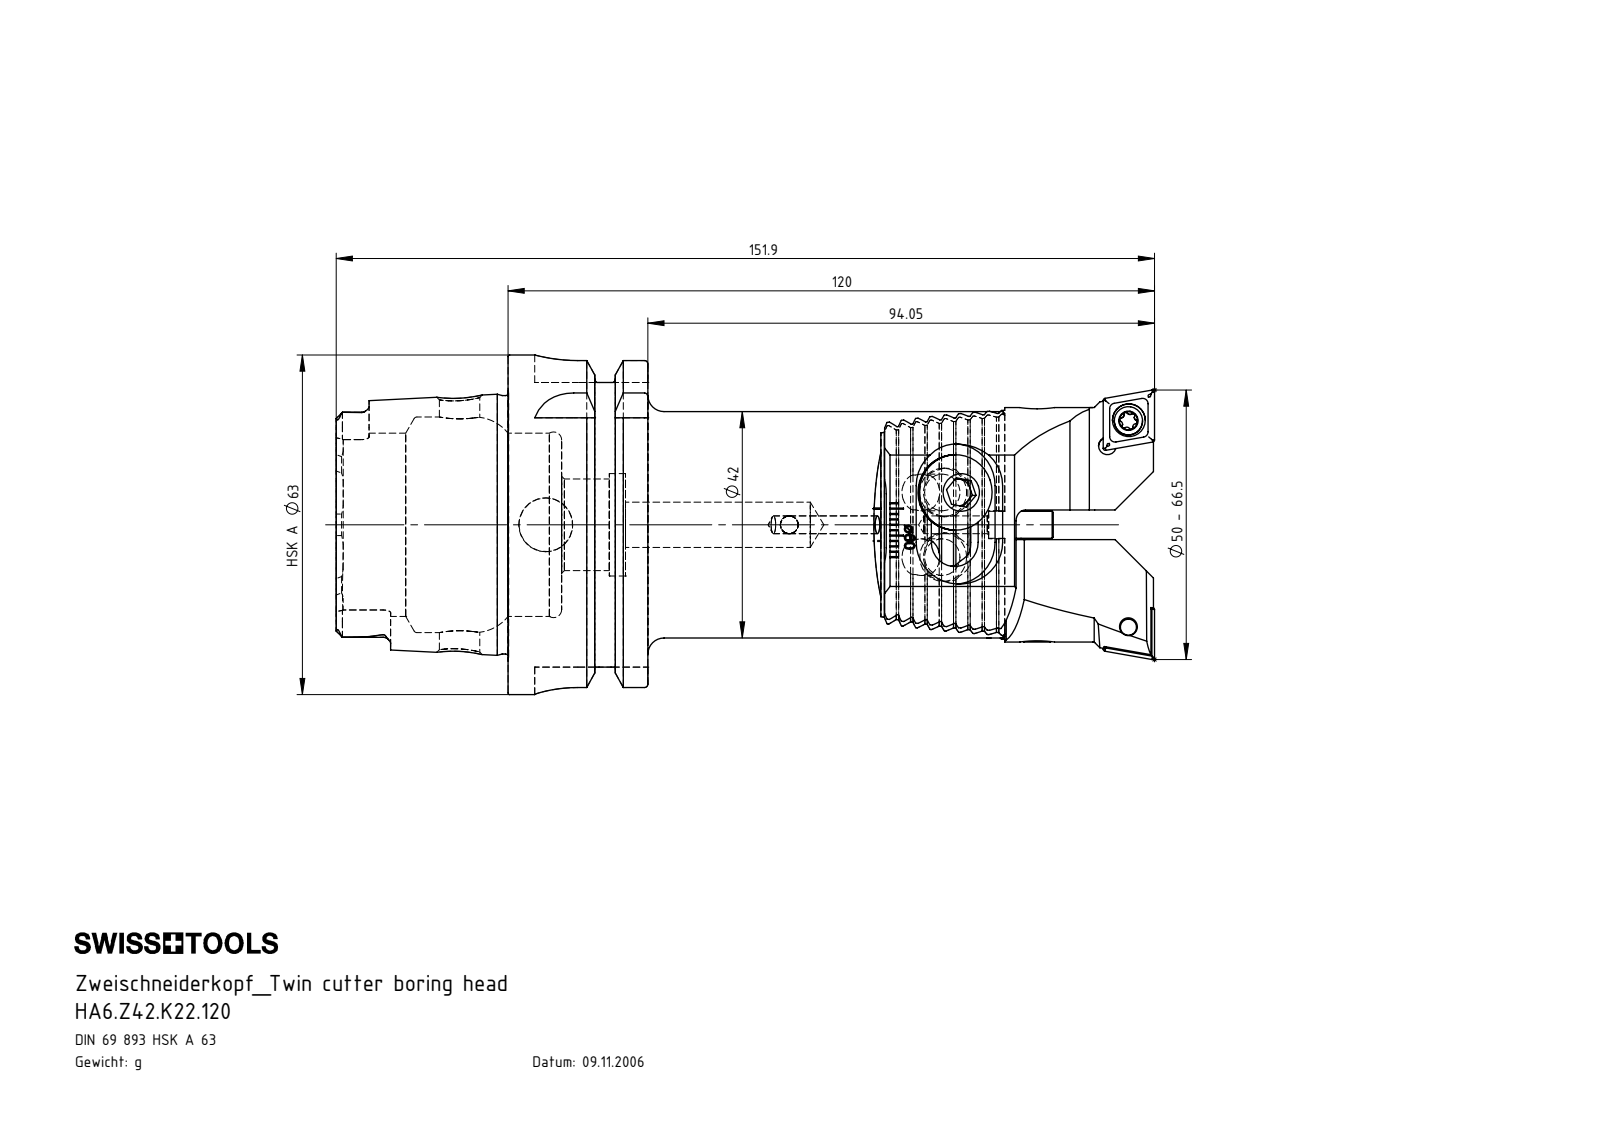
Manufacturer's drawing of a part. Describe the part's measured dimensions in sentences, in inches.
The part is named "HA6.Z42.K22.120; Z42-ER1.002.020_A; Z42-ER1.001.020; Z42-ER1.003.020_A_gespannt (+1 more)". Its 3-D file was written by "SolidWorks 2022 (CONFIG_CONTROL_DESIGN)". It is 5 solids with 408 faces: 183 planar, 120 cylindrical and 105 other. Overall it measures 4.886 by 2.48 by 2.48 inches. Its volume is 9.513 cubic inches and its surface area 55.14 square inches. Round holes: 4 of diameter 0.13, 3 of diameter 0.331, 2 of diameter 0.268, 2 of diameter 0.354, 1 of diameter 0.295, 1 of diameter 0.394, 1 of diameter 0.669, 1 of diameter 0.748, 1 of diameter 1.339, 1 of diameter 1.575. Round bosses or shafts: 2 of diameter 0.551, 2 of diameter 0.315, 1 of diameter 2.48, 1 of diameter 2.163, 1 of diameter 1.887, 1 of diameter 1.654. Partial cylindrical surfaces (rounded edges, fillets, slot ends): 18 of radius 0.008, 6 of radius 0.055, 4 of radius 0.113, 4 of radius 0.315, 2 of radius 8.661. The main face-to-face distances are 0.094, 0.187, 1.022, 0.469, 0.375, 0.281, 0.563, 0.63, 0.281, 0.392. The hole center spacings are 1.78.
